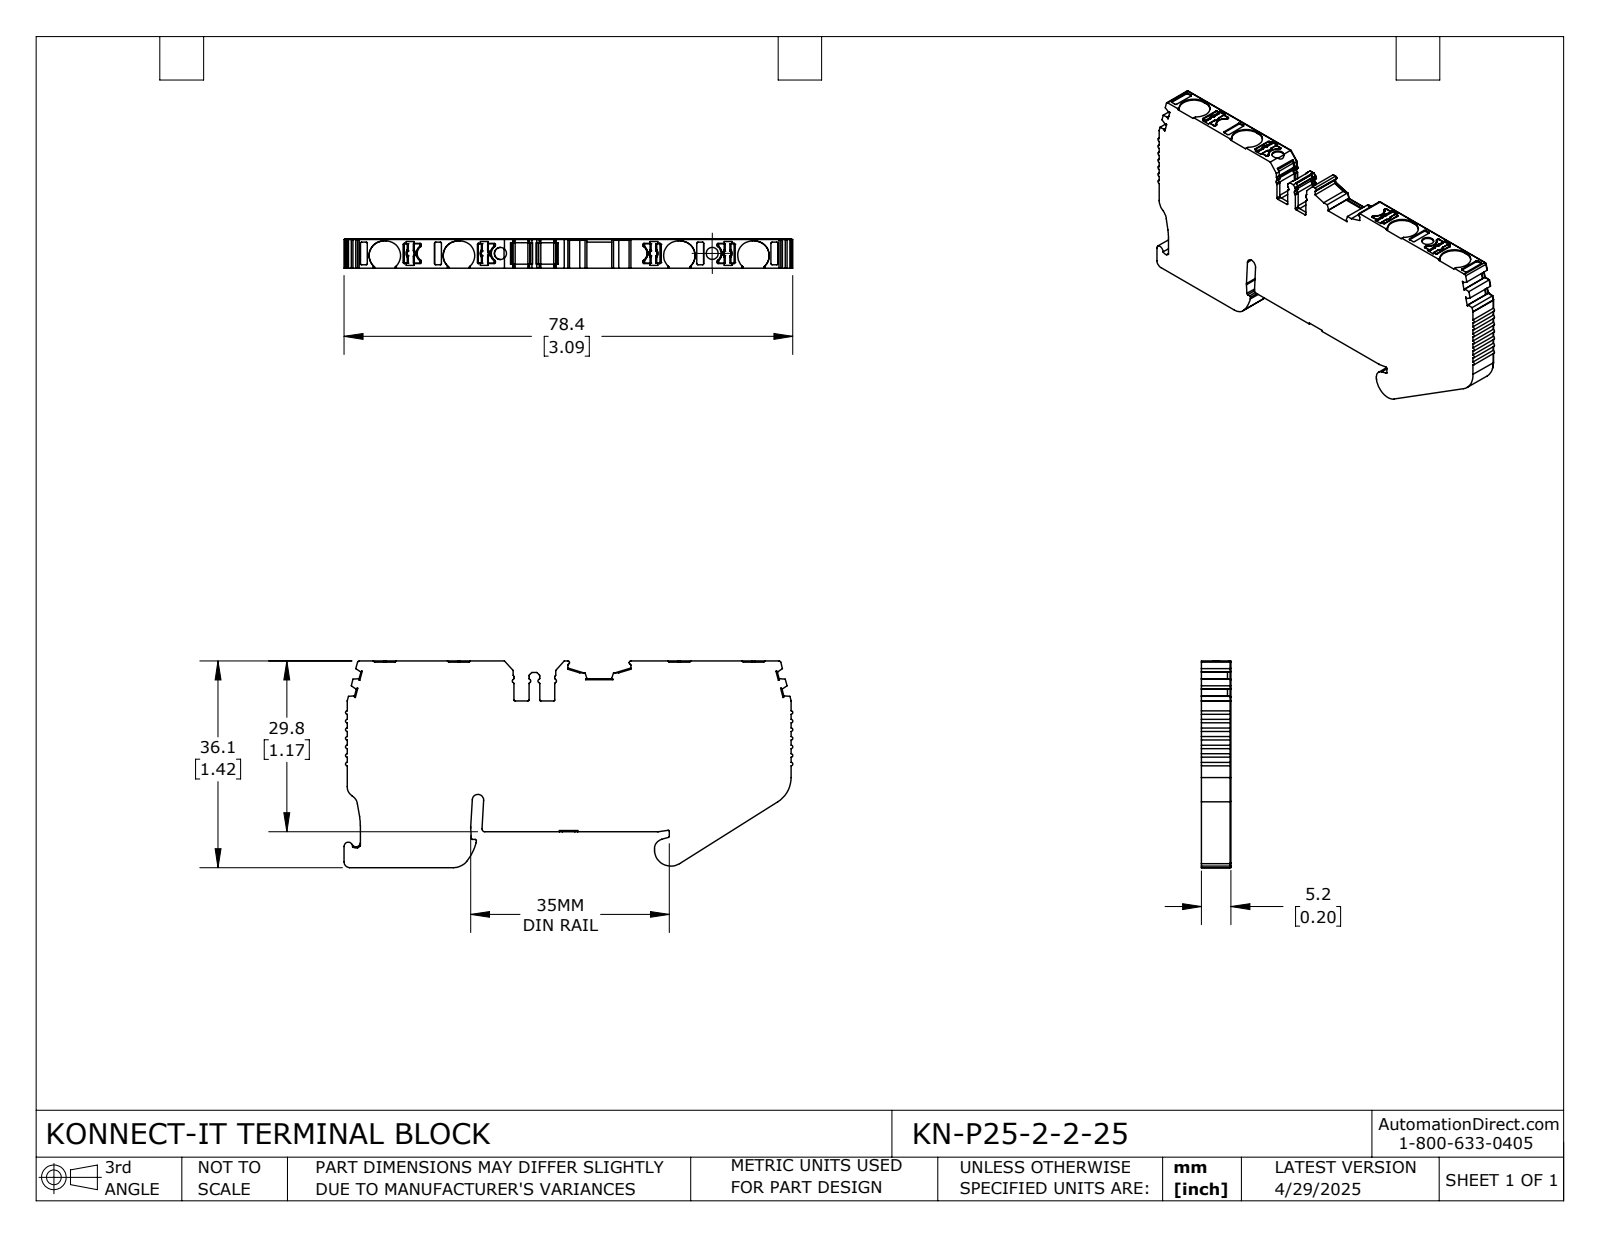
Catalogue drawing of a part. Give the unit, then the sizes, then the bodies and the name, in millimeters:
Units: millimetres
Overall size (bounding box): 78.4 × 36.1 × 5.2
Round holes (diameter × count): ⌀2.1 ×2
Partial cylindrical surfaces — rounded edges, fillets, slot ends (radius × count): R0.2 ×78, R0.3 ×39, R0.1 ×21, R0.5 ×18, R0.2 ×16, R0.4 ×9, R2.5 ×8, R1.5 ×4
Main face-to-face distances: 5.2, 29.6, 29.8, 6.2, 35.9, 36.1, 77.5, 1.2, 5, 4.5
Hole centre spacings: 37
Volume: 12 000 mm³ · Surface area: 6 217 mm²
Bodies: 1 solid, 743 faces (381 planar, 291 cylindrical, 71 other)
Part name (STEP PRODUCT): KN-P25-2-2-25
STEP written by: SolidWorks 2024 (CONFIG_CONTROL_DESIGN)
